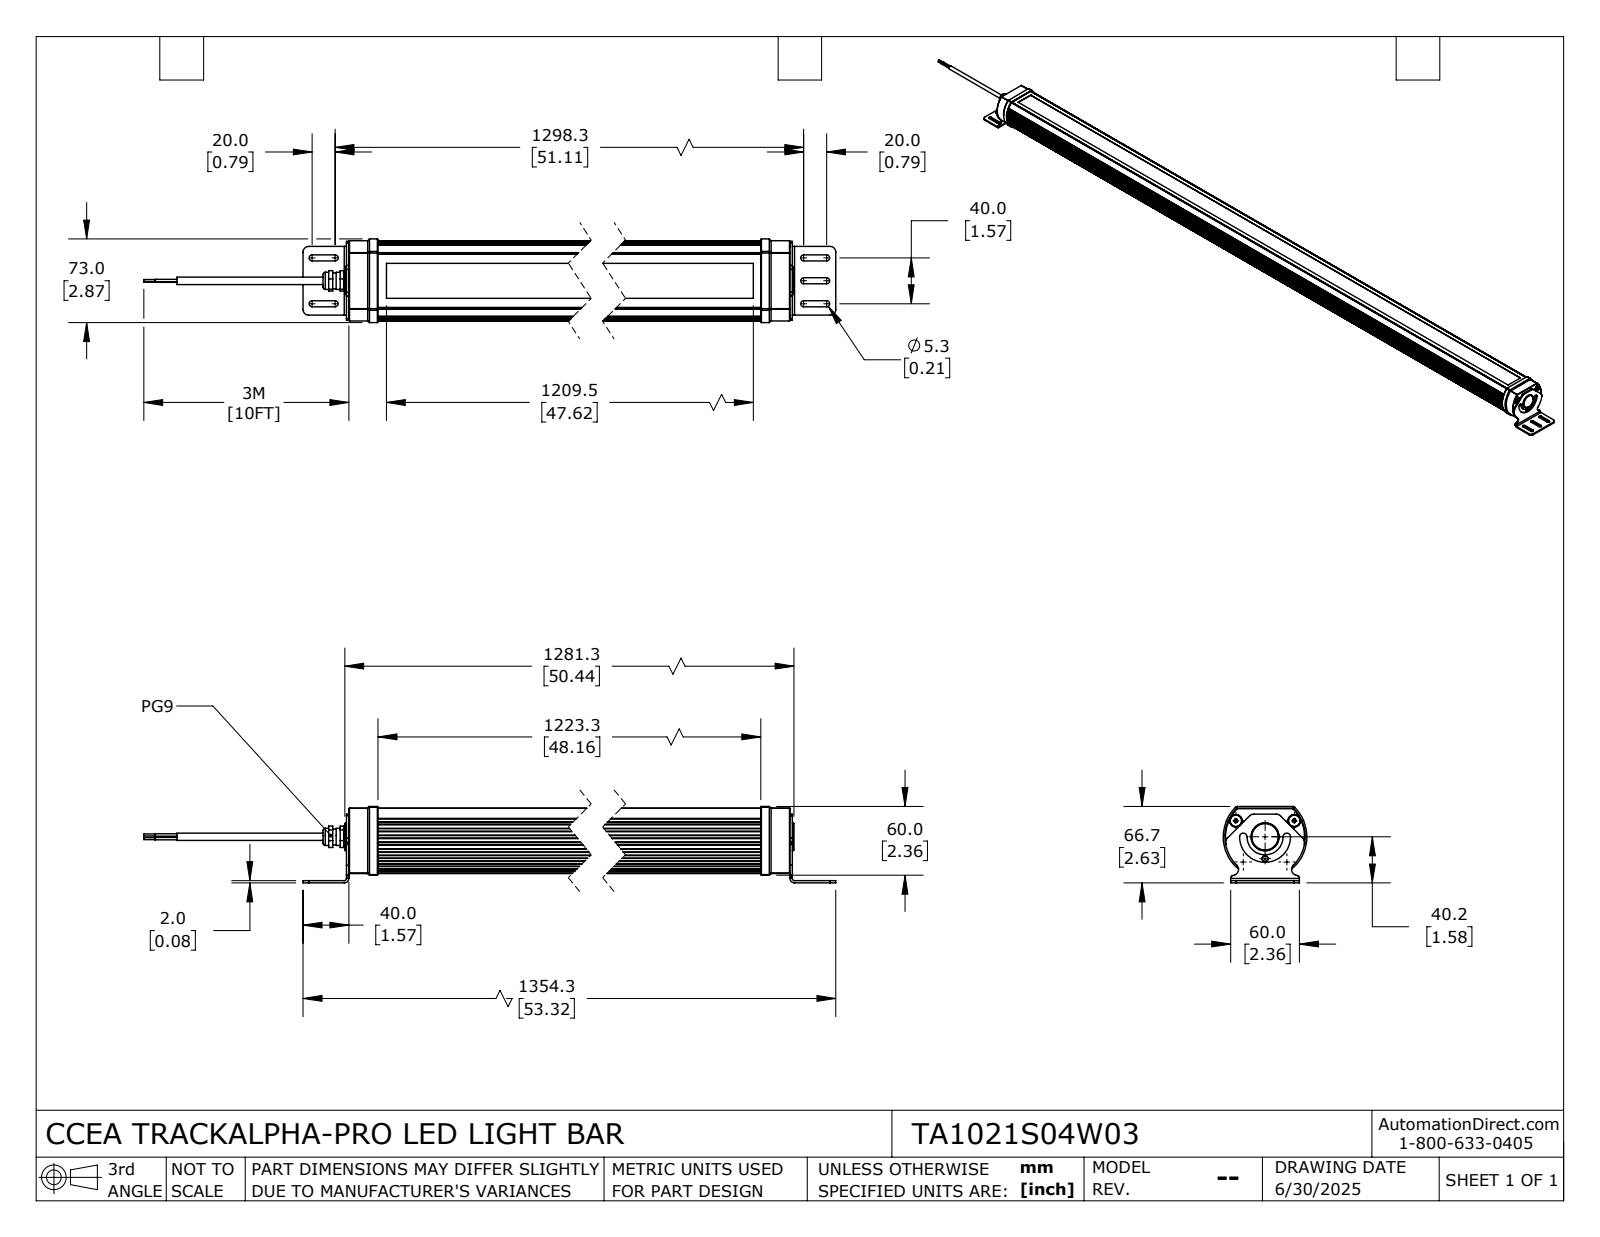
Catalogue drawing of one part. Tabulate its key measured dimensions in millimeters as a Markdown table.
| quantity | value |
| --- | --- |
| part name | TA1021S04W03 |
| STEP written by | SolidWorks 2024 (CONFIG_CONTROL_DESIGN) |
| units | millimeters |
| bodies | 3 solids, 695 faces (238 planar, 331 cylindrical, 126 other) |
| overall size | 1493.3 × 73 × 66.7 |
| volume | 4 328 000 mm³ |
| surface area | 397 700 mm² |
| round holes (diameter × count) | 5.5 × 4, 1.1 × 2, 3 × 2, 10 × 2, 4.9 × 1, 7 × 1, 14 × 1, 24.5 × 1, 27 × 1 |
| round bosses / shafts (diameter × count) | 10 × 4, 5 × 4, 3 × 2, 2.1 × 2, 1.7 × 2, 1.6 × 2, 1 × 2, 24 × 1 |
| partial cylindrical surfaces (radius × count) | 0.5 × 22, 0.3 × 16, 5 × 13, 2.6 × 12, 1.5 × 10, 1.9 × 8, 2 × 8, 0.7 × 2 |
| main face-to-face distances | 56.9, 56.9, 46.8, 5, 51.9, 0.5, 5.1, 5.5, 51.4, 5.6 |
| hole center spacings | 8.5, 12.8, 18.4, 19.2, 21.1, 24.1, 25.2, 29.1 |
